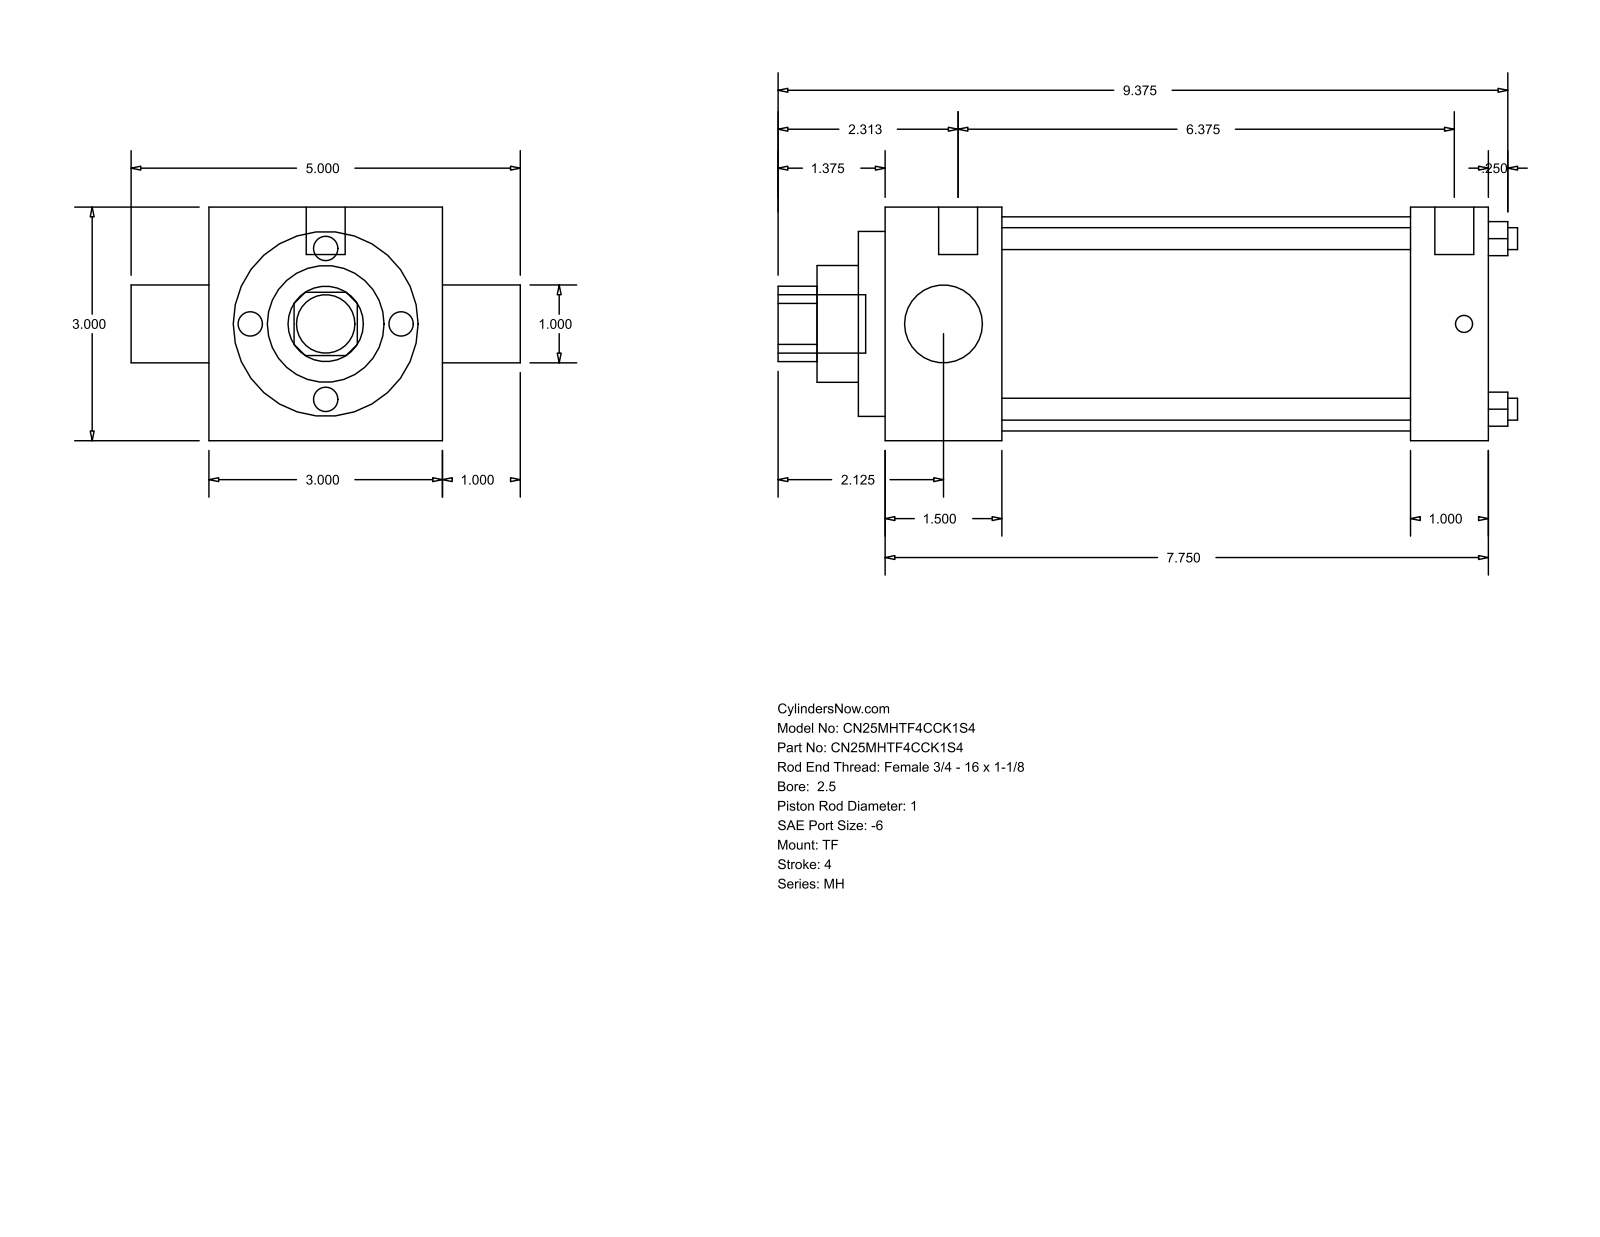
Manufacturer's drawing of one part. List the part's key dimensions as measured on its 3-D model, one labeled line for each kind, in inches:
Part name (STEP PRODUCT): MH_TF__0250_1
STEP written by: GSSL Pune (CONFIG_CONTROL_DESIGN)
Units: inches
Bodies: 0 solids, 86 faces (61 planar, 25 cylindrical, 0 other)
Overall size (bounding box): 9.5 × 5 × 3
Round holes (diameter × count): ⌀0.281 ×4, ⌀1 ×2, ⌀1.5 ×1, ⌀2.375 ×1, ⌀2.75 ×1
Round bosses / shafts (diameter × count): ⌀0.219 ×3, ⌀0.5 ×2, ⌀0.75 ×1
Partial cylindrical surfaces — rounded edges, fillets, slot ends (radius × count): R0.484 ×1
Main face-to-face distances: 3, 7.75, 1, 1.5, 6.25, 6.75, 5.25, 0.344, 1.844, 7.094
Hole centre spacings: 1.548, 2.19, 3.097
